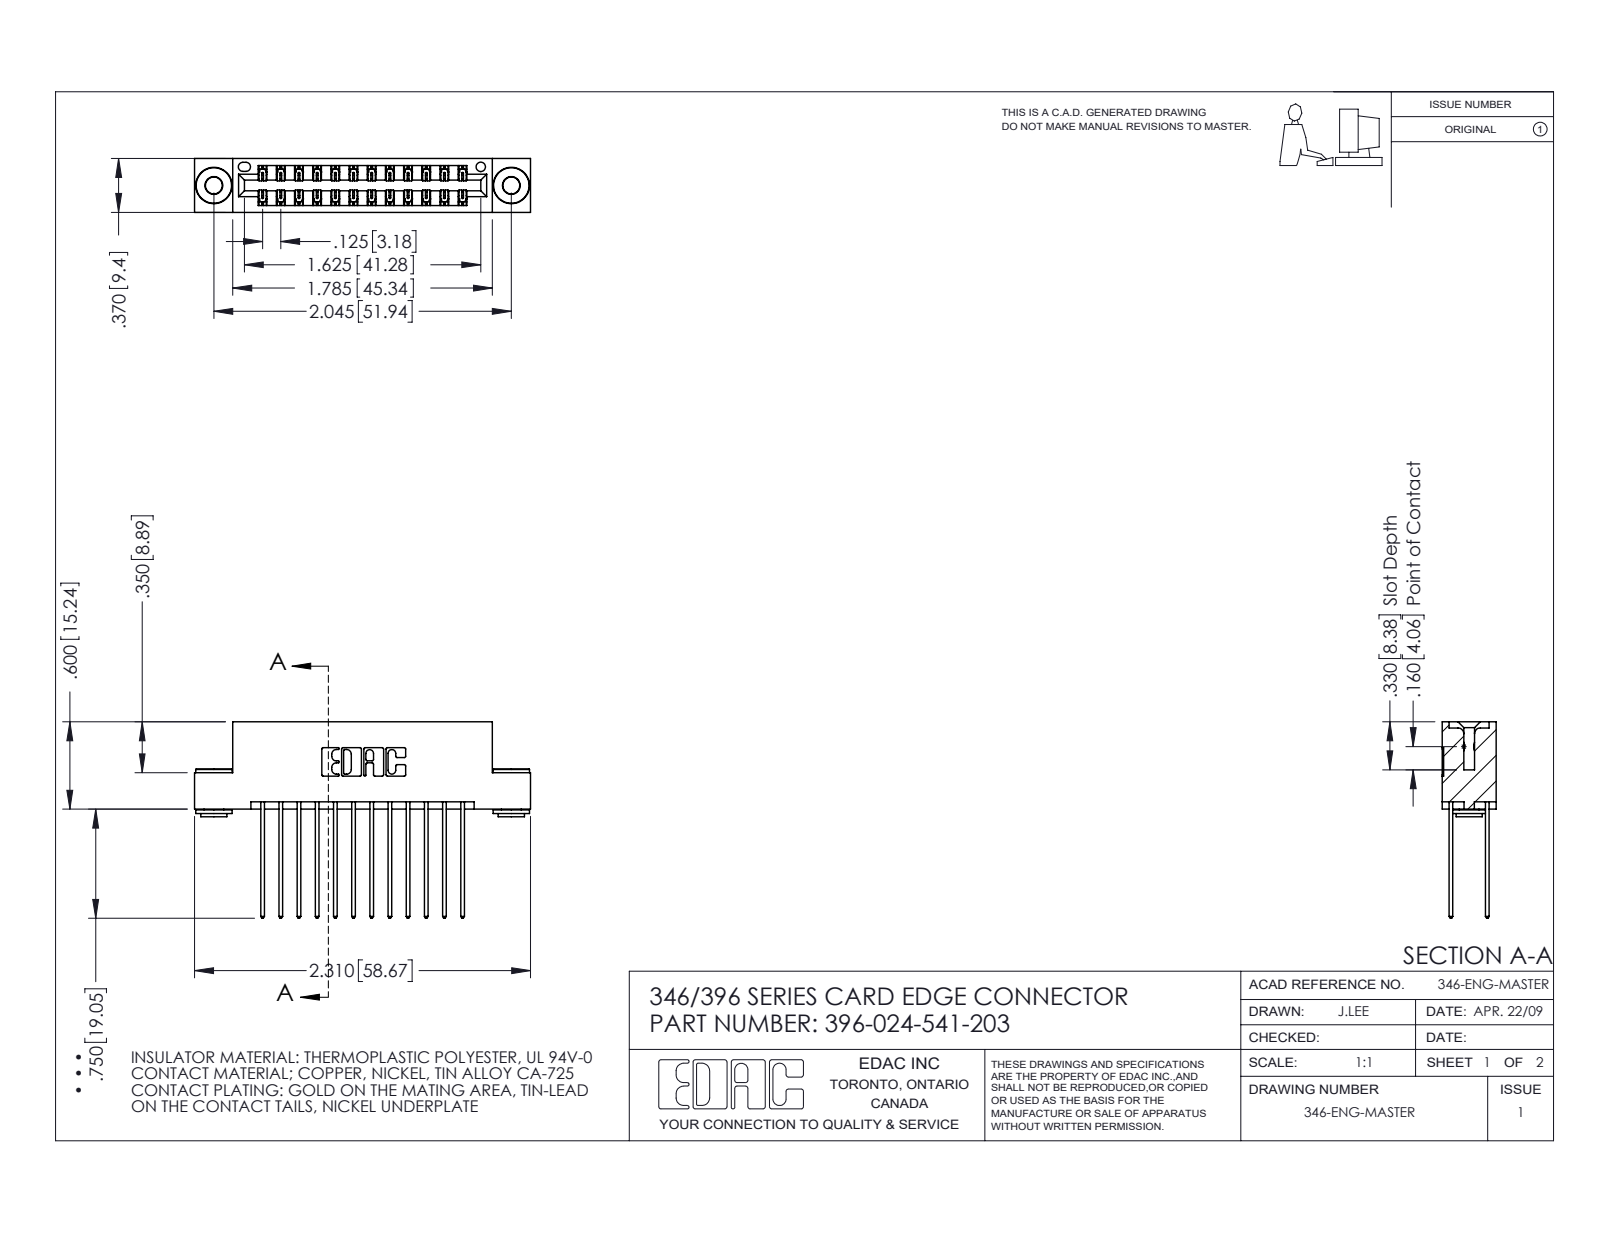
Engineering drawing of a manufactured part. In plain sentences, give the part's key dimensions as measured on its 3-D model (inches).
The part is named "346 Part_Flush Mounting Lugs - 0.156 Dia-TH; 345-292-001_345-293-141; 396-024-541-203; 345-250-002_345-250-002-102". Its 3-D file was written by "SolidWorks 2016 (CONFIG_CONTROL_DESIGN)". It is 27 solids with 1408 faces: 926 planar, 474 cylindrical and 8 other. Overall it measures 2.31 by 1.35 by 0.37 inches. Its volume is 0.345 cubic inches and its surface area 12.65 square inches. Round holes: 2 of diameter 0.116, 2 of diameter 0.156, 1 of diameter 0.064. Round bosses or shafts: 2 of diameter 0.25, 2 of diameter 0.18, 2 of diameter 0.136. Partial cylindrical surfaces (rounded edges, fillets, slot ends): 36 of radius 0.006, 24 of radius 0.01, 22 of radius 0.01, 6 of radius 0.007, 6 of radius 0.031, 3 of radius 0.026, 2 of radius 0.014, 2 of radius 0.022. The main face-to-face distances are 0.25, 0.048, 0.322, 0.025, 0.072, 0.298, 0.37, 0.275, 0.225, 0.148. The hole center spacings are 0.246, 1.839, 2.045.
